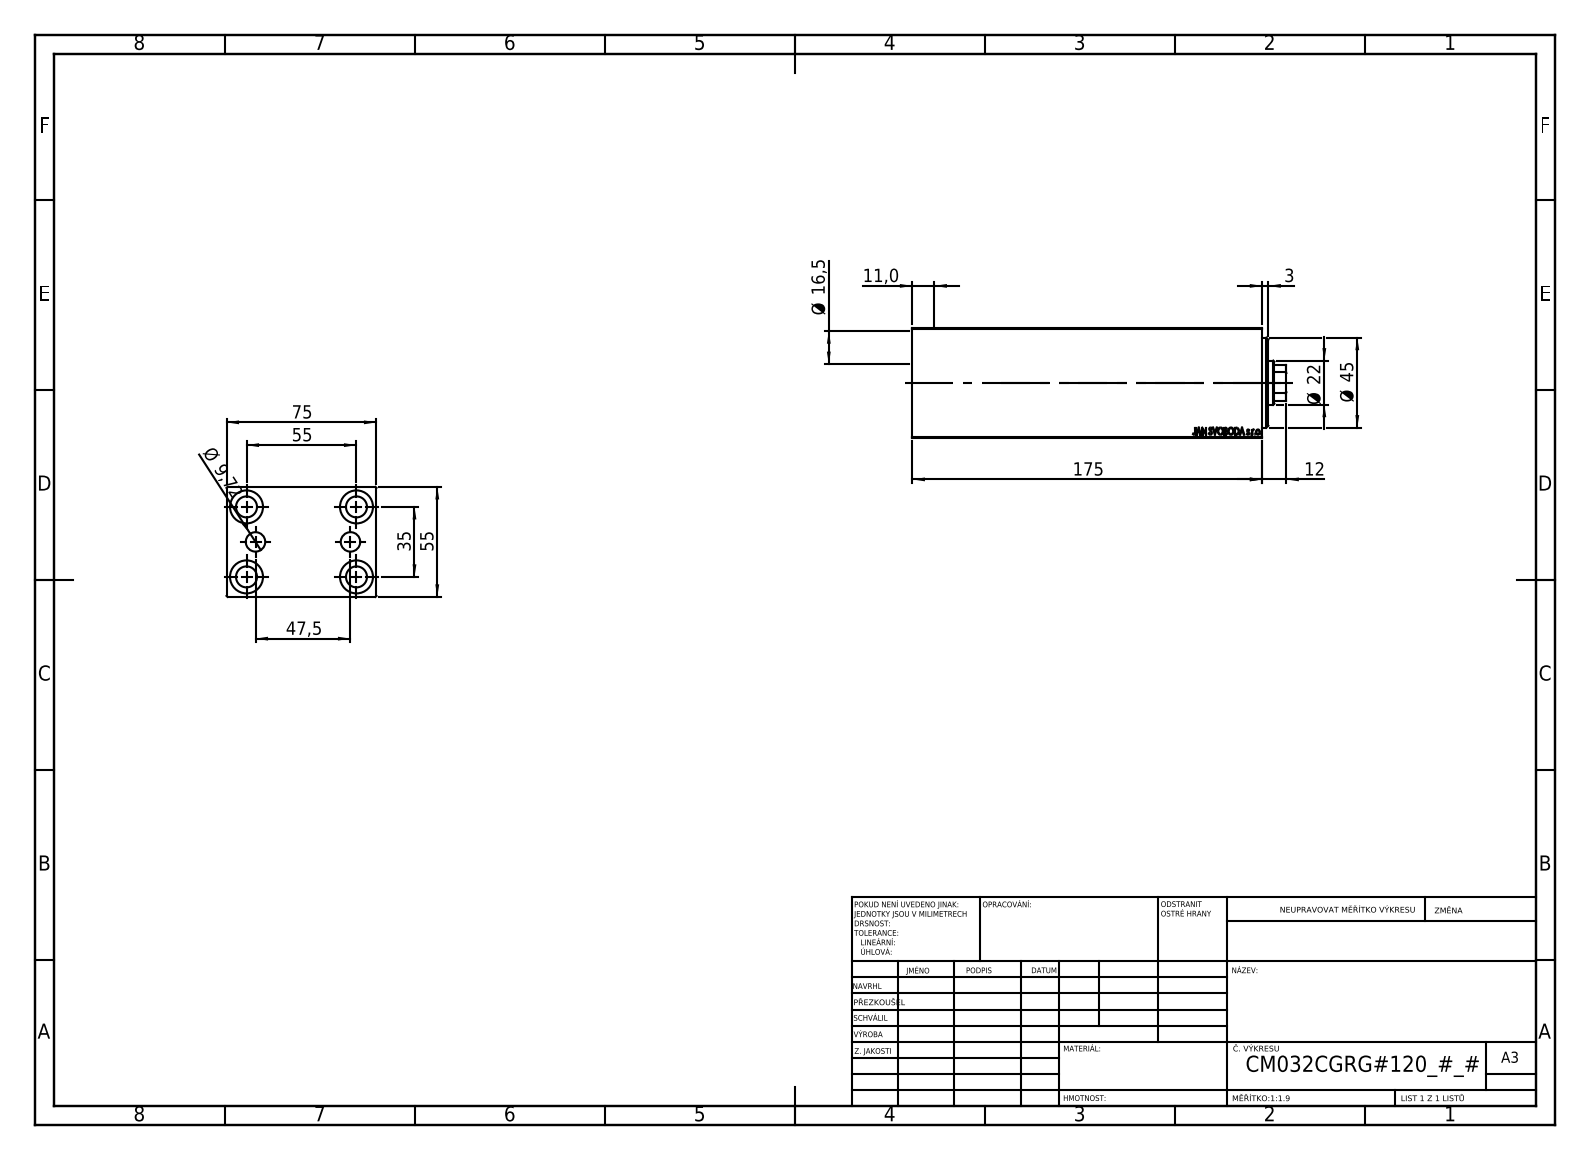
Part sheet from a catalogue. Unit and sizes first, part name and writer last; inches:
Units: inches
Overall size (bounding box): 7.362 × 2.953 × 2.165
Round holes (diameter × count): ⌀0.413 ×5, ⌀0.65 ×4, ⌀0.383 ×2, ⌀0.866 ×1, ⌀1.004 ×1, ⌀1.26 ×1, ⌀1.339 ×1, ⌀1.772 ×1
Partial cylindrical surfaces — rounded edges, fillets, slot ends (radius × count): R0.413 ×1
Main face-to-face distances: 2.165, 2.953, 0.394, 6.496, 6.89, 6.693, 0.197, 6.299, 6.024, 0.433
Hole centre spacings: 1.283, 0.699, 0.711, 1.378, 2.104, 2.16, 2.165, 2.567
Volume: 36.82 in³ · Surface area: 179.5 in²
Bodies: 3 solids, 852 faces (406 planar, 52 cylindrical, 394 other)
Part name (STEP PRODUCT): V450CM_C_Body; V450CM_VC_B; V450CM_C_VCP
STEP written by: SolidWorks 2019 (CONFIG_CONTROL_DESIGN)
